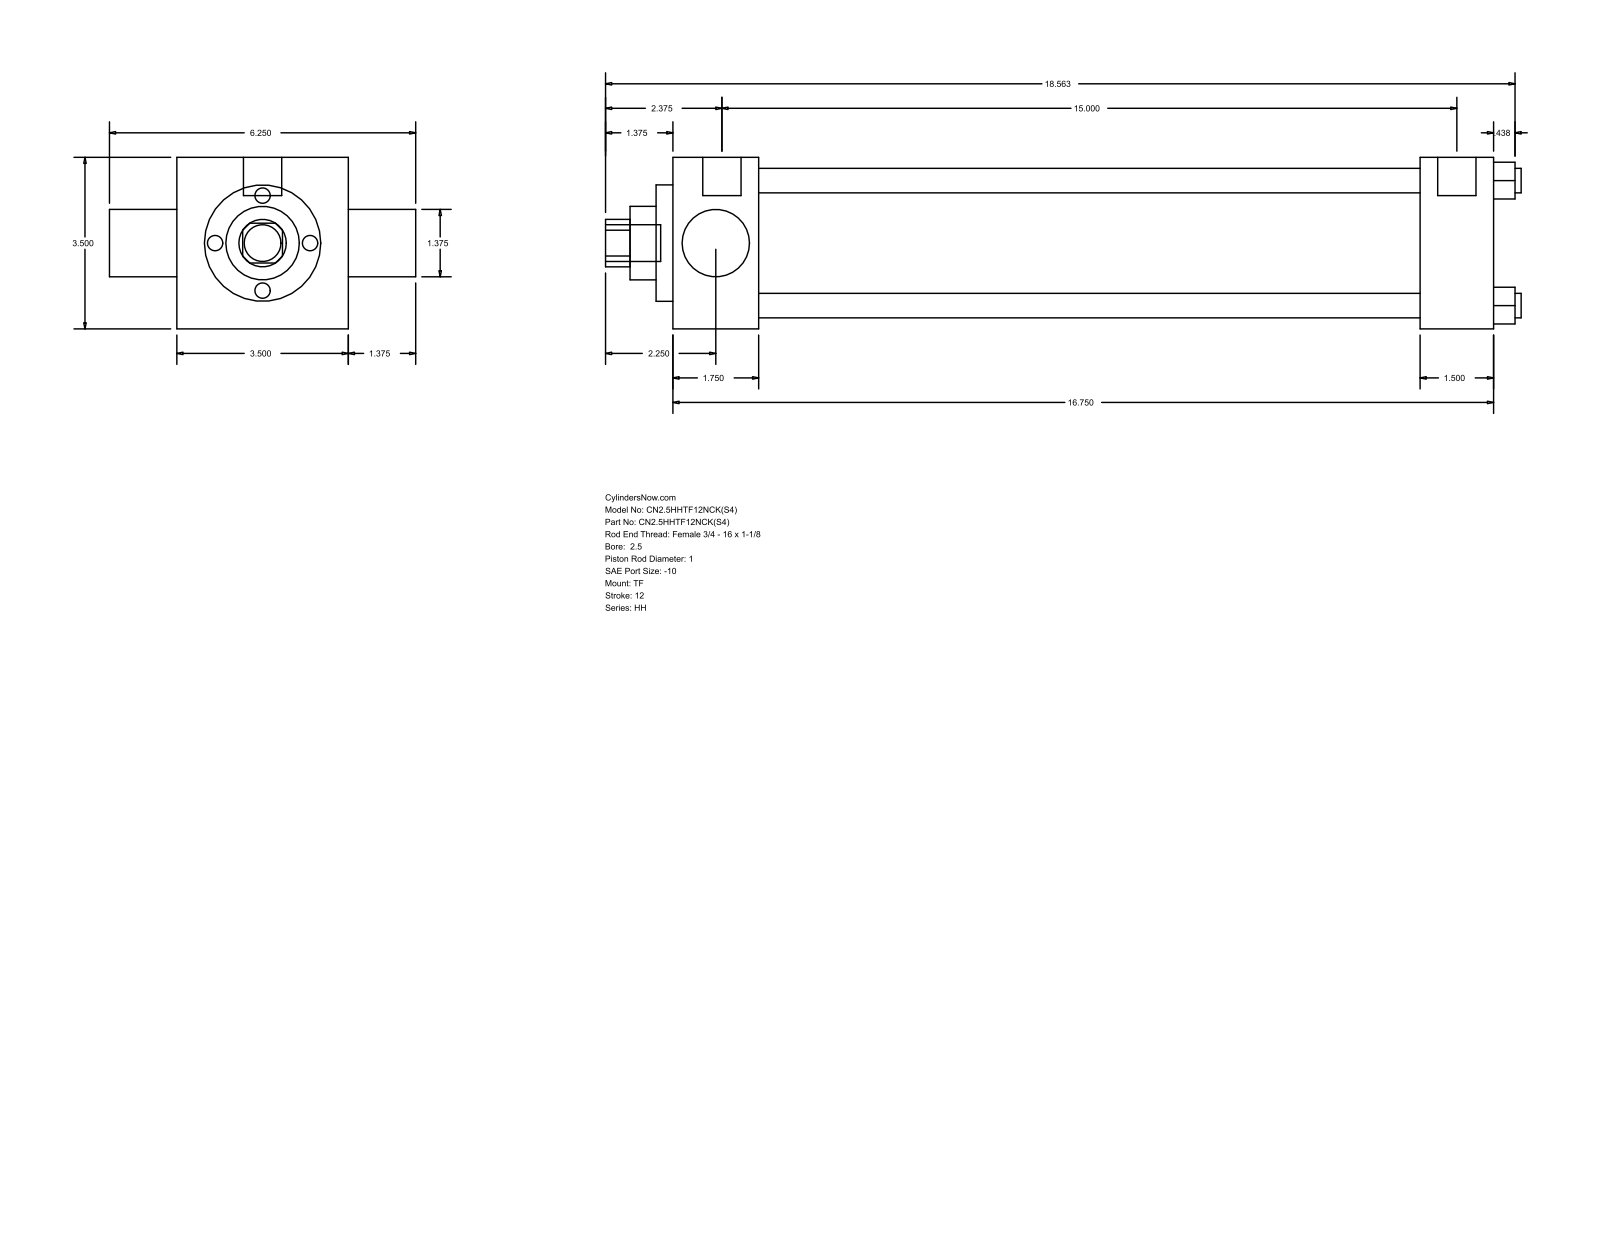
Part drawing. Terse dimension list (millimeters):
name: HH_TF__0250_1
written by: GSSL Pune (CONFIG_CONTROL_DESIGN)
unit: mm
bodies: 0 solids, 86 faces (61 planar, 25 cylindrical, 0 other)
size: 474.66 × 158.75 × 88.9
holes: 4× ⌀12.7, 1× ⌀25.4, 1× ⌀34.92, 1× ⌀38.1, 1× ⌀60.33, 1× ⌀73.03
bosses: 3× ⌀5.56, 2× ⌀19.84, 1× ⌀19.05
rounds: 1× R12.29
face distances: 88.9, 425.46, 44.46, 381, 387.35, 342.89, 38.11, 34.93, 123.83, 8.73
hole spacings: 45.79, 64.76, 91.58
